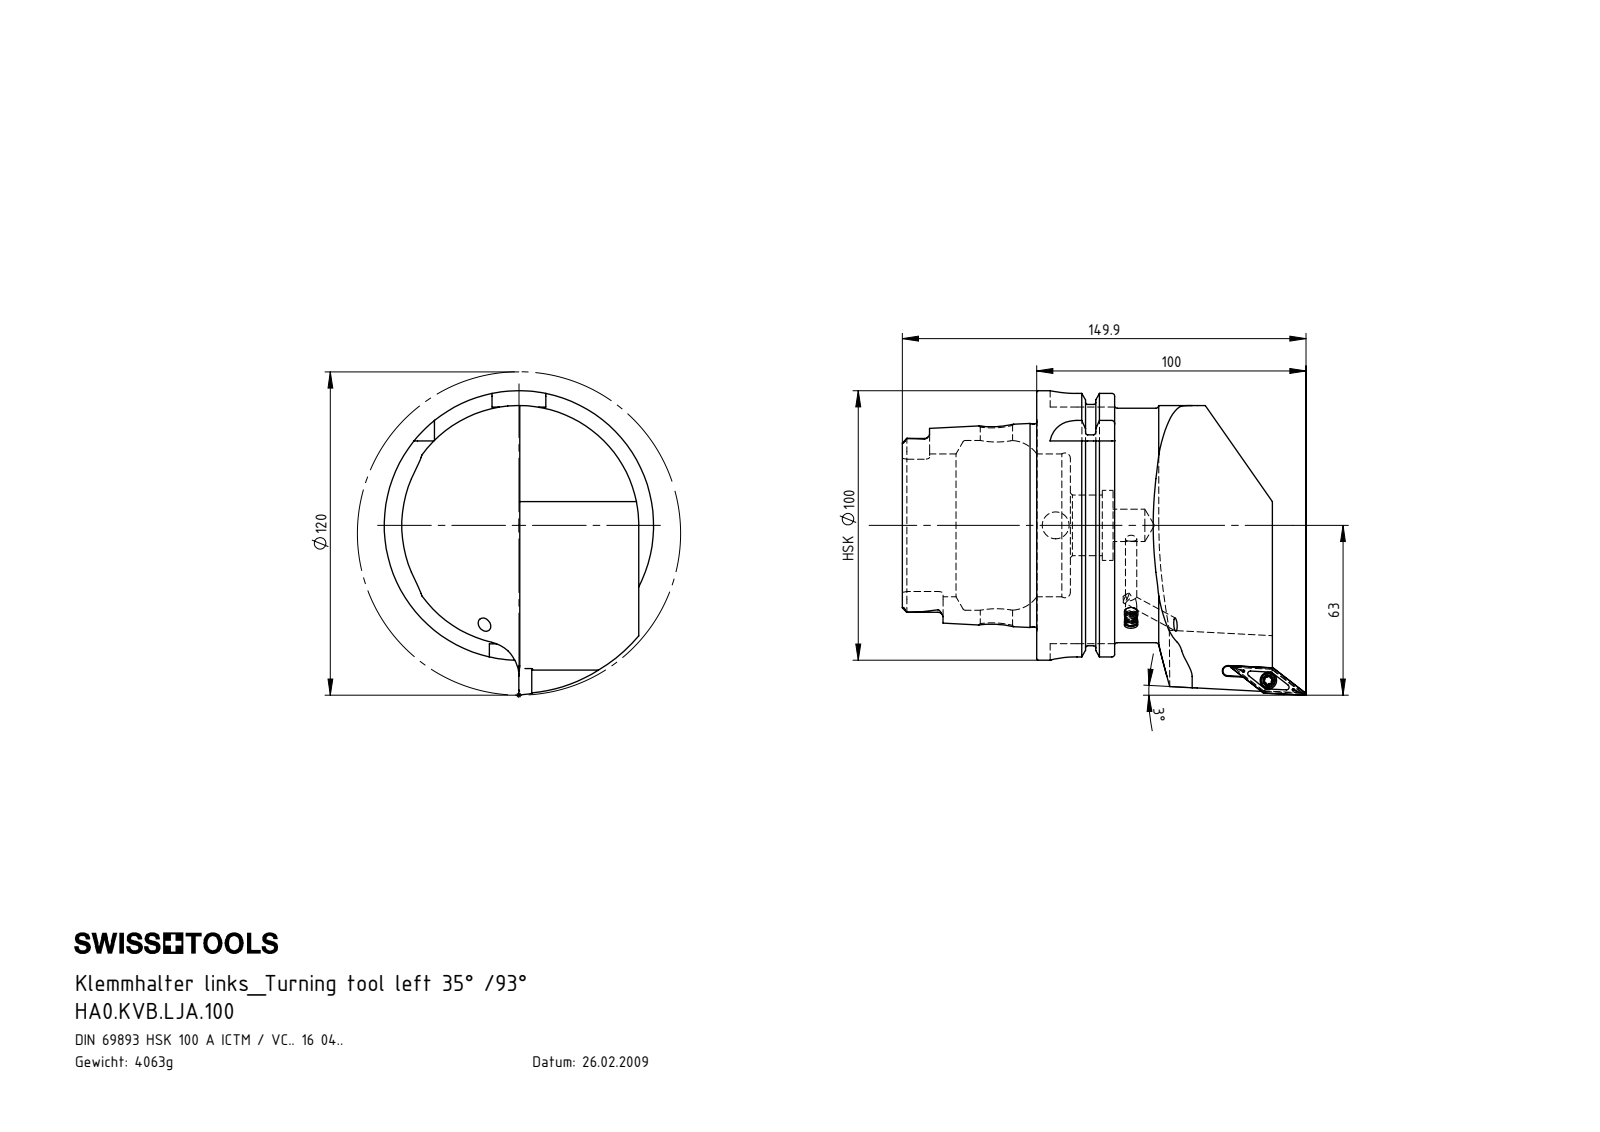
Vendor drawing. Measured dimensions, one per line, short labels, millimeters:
name: HA0.KVB.LJA.100; KVT_MB_600_050; WCB-ER2.001.009_A; VCMT160404 (+1 more)
written by: SolidWorks 2012 (AUTOMOTIVE_DESIGN)
unit: mm
bodies: 5 solids, 309 faces (77 planar, 91 cylindrical, 141 other)
size: 149.93 × 113 × 100
volume: 517 130 mm³; area: 67 934 mm²
holes: 2× ⌀4.2, 2× ⌀12, 1× ⌀3.3, 1× ⌀4, 1× ⌀4.4, 1× ⌀6.1, 1× ⌀10, 1× ⌀22.5, 1× ⌀26, 1× ⌀53, 1× ⌀63
bosses: 1× ⌀100, 1× ⌀91.95, 1× ⌀87, 1× ⌀75.26, 1× ⌀5.25, 1× ⌀5, 1× ⌀4
rounds: 6× R0.34, 6× R0.59, 6× R1.9, 4× R10, 2× R4.83, 2× R4.88, 1× R1.75, 1× R6
face distances: 87.5, 44.2, 12.45, 75.05, 28.95, 16.5, 58.55, 49.9, 62.35, 78.85
hole spacings: 97.62, 97.73
